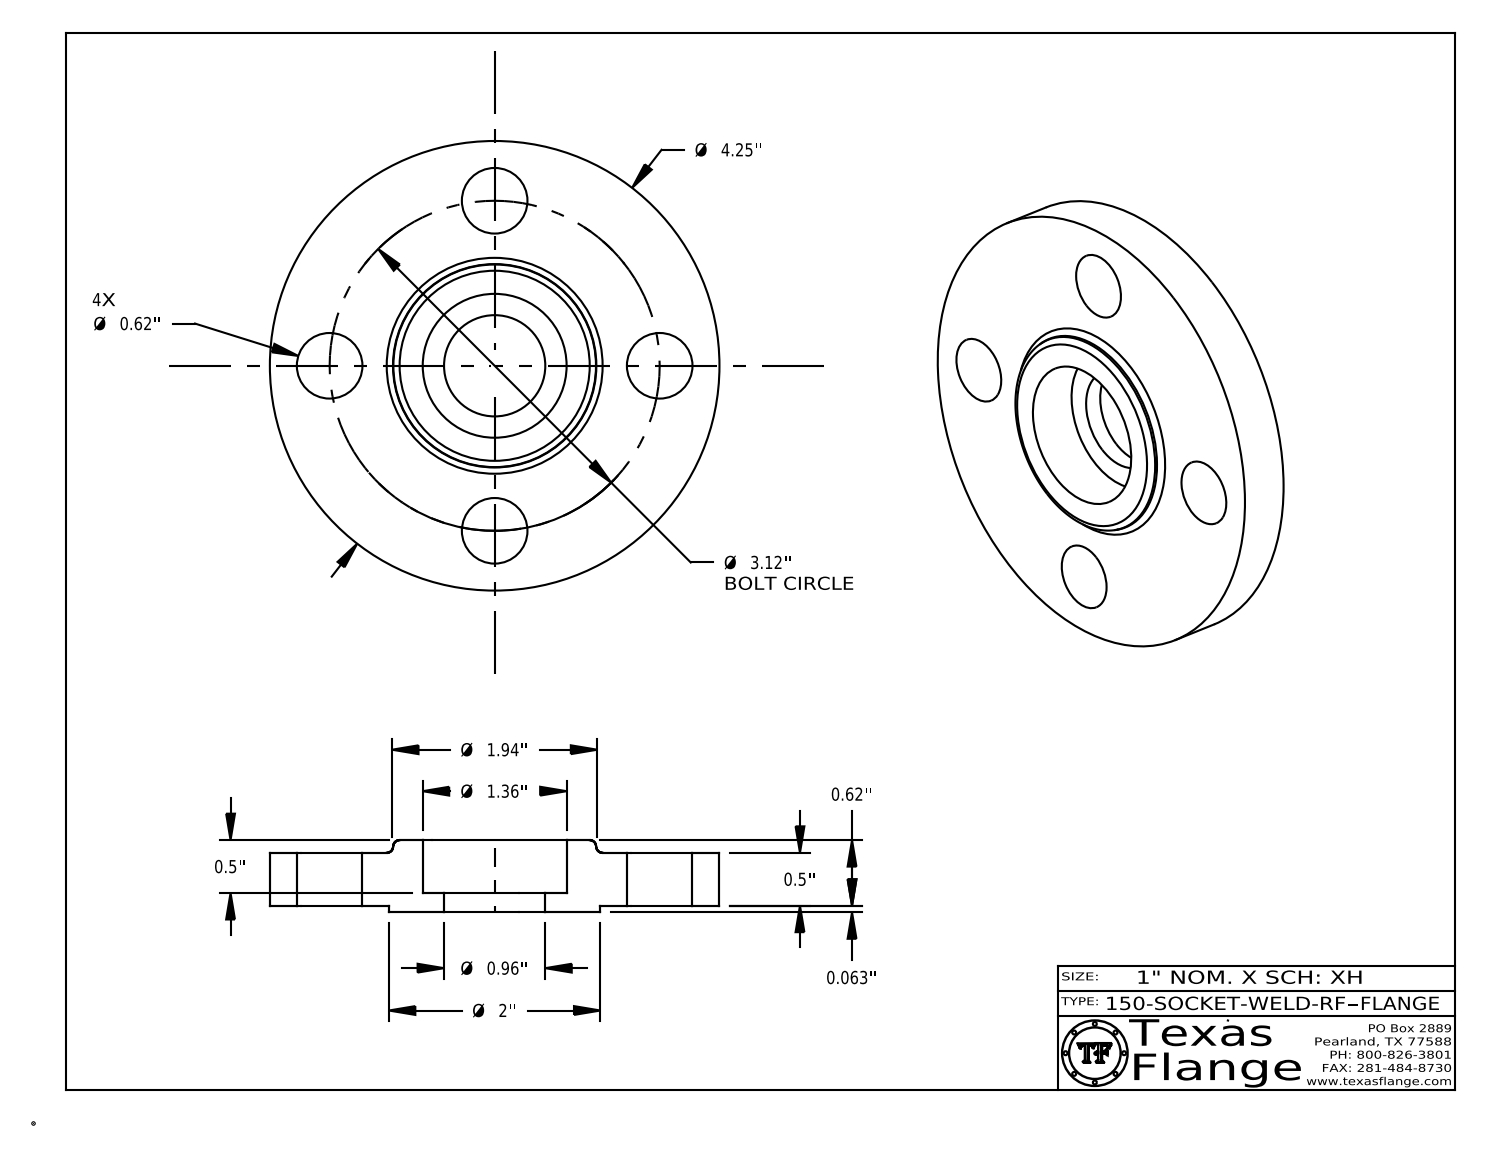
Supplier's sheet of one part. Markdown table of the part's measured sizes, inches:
| quantity | value |
| --- | --- |
| part name | 150-SOCKET-WELD-RF |
| STEP written by | CATIA V5 STEP AP214 (AUTOMOTIVE_DESIGN) |
| units | inches |
| bodies | 1 solid, 412 faces (370 planar, 36 cylindrical, 6 other) |
| overall size | 4.25 × 4.25 × 0.683 |
| volume | 6.174 in³ |
| surface area | 38.66 in² |
| round holes (diameter × count) | 0.62 × 4, 0.495 × 1, 0.957 × 1, 1.36 × 1 |
| round bosses / shafts (diameter × count) | 0.03 × 8, 4.25 × 1, 2 × 1, 0.39 × 1 |
| main face-to-face distances | 0.5, 0.063, 0.563, 0.12, 0.683, 0.62, 0.183, 0.38, 0.548, 0.485 |
| hole center spacings | 1.56, 2.206, 1.194, 2.882, 3.12, 1.56 |
